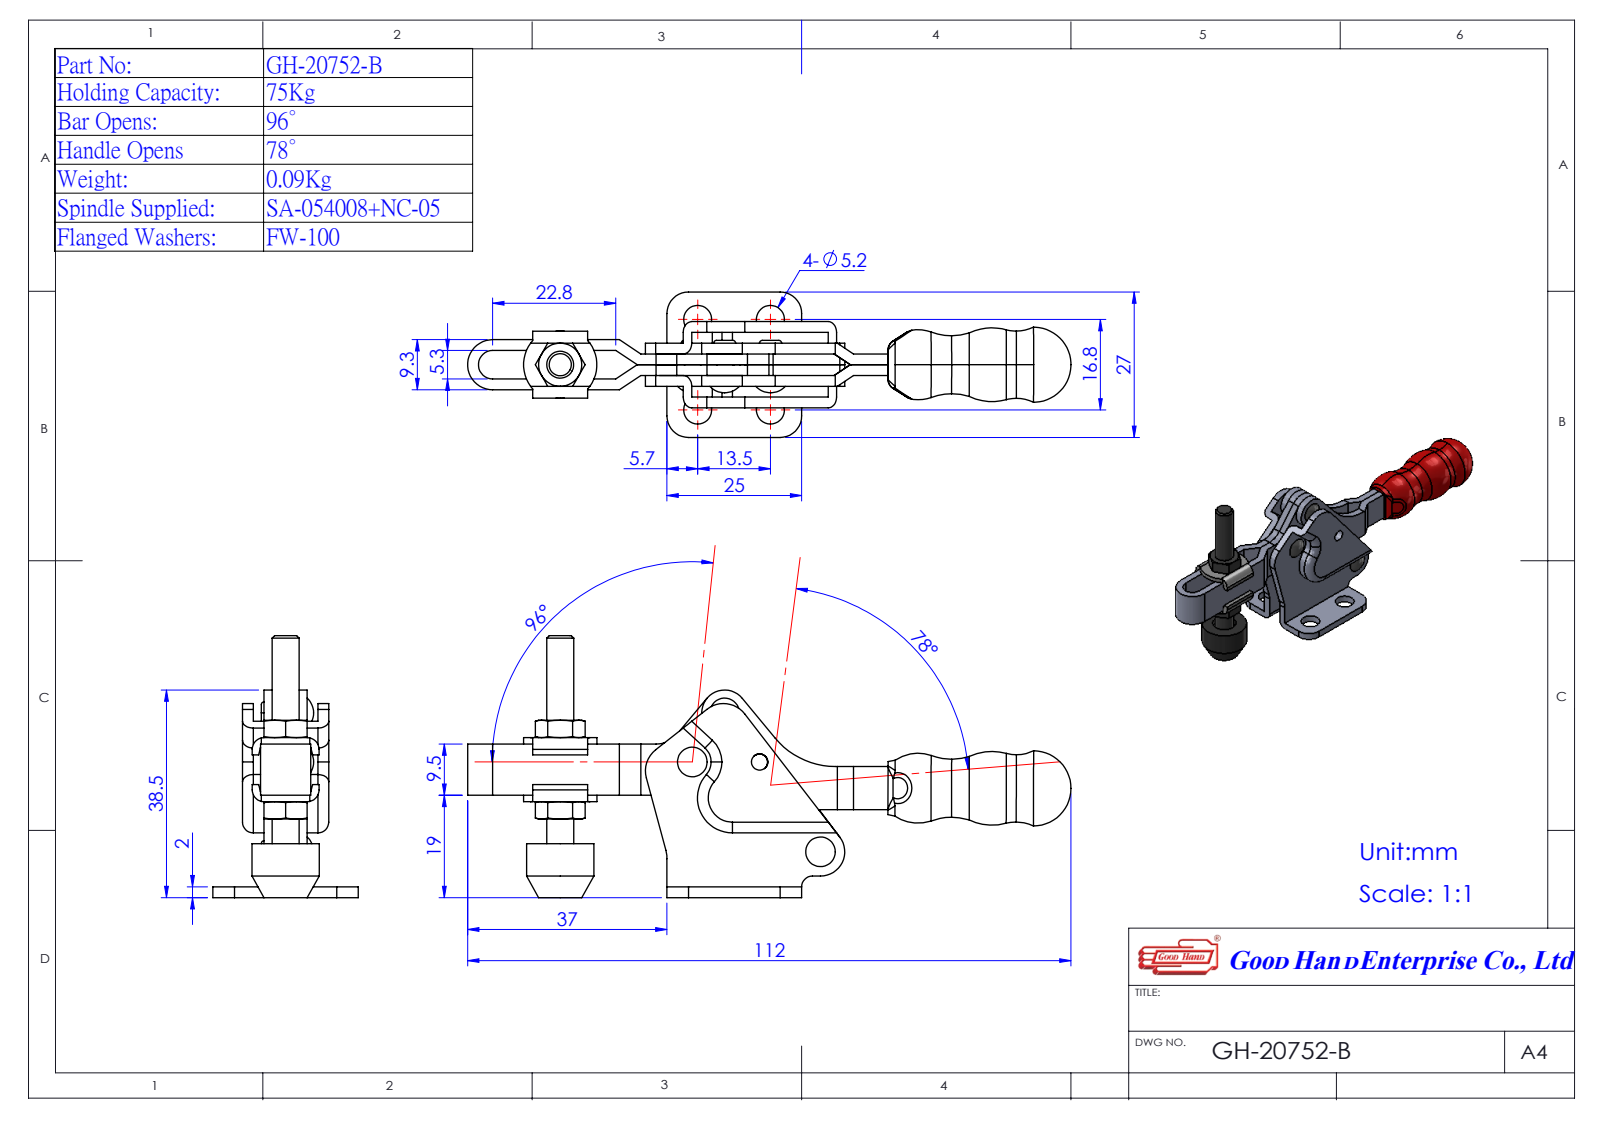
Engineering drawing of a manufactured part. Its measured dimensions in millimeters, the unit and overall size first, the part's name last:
Units: millimetres
Overall size (bounding box): 112 × 48.58 × 27
Round holes (diameter × count): ⌀2.5 ×4, ⌀5.2 ×4
Round bosses / shafts (diameter × count): ⌀3.05 ×2, ⌀12.5 ×1, ⌀5 ×1
Partial cylindrical surfaces — rounded edges, fillets, slot ends (radius × count): R1 ×7, R2.2 ×4, R4 ×4, R5 ×4, R4.5 ×3, R2 ×1, R2.65 ×1, R3.5 ×1
Main face-to-face distances: 2, 4, 6, 8, 10, 12, 3.35, 1.35, 0.65, 2.65
Hole centre spacings: 13.5, 16.8, 21.55, 10.9, 15.16, 15.44, 15.89, 29.05
Volume: 16 171 mm³ · Surface area: 14 524 mm²
Bodies: 5 solids, 267 faces (128 planar, 105 cylindrical, 34 other)
Part name (STEP PRODUCT): Group5^493784(GH-20752-B); Group4^493784(GH-20752-B); Group1^493784(GH-20752-B); 493784(GH-20752-B) (+2 more)
STEP written by: SolidWorks 2016 (AUTOMOTIVE_DESIGN)
